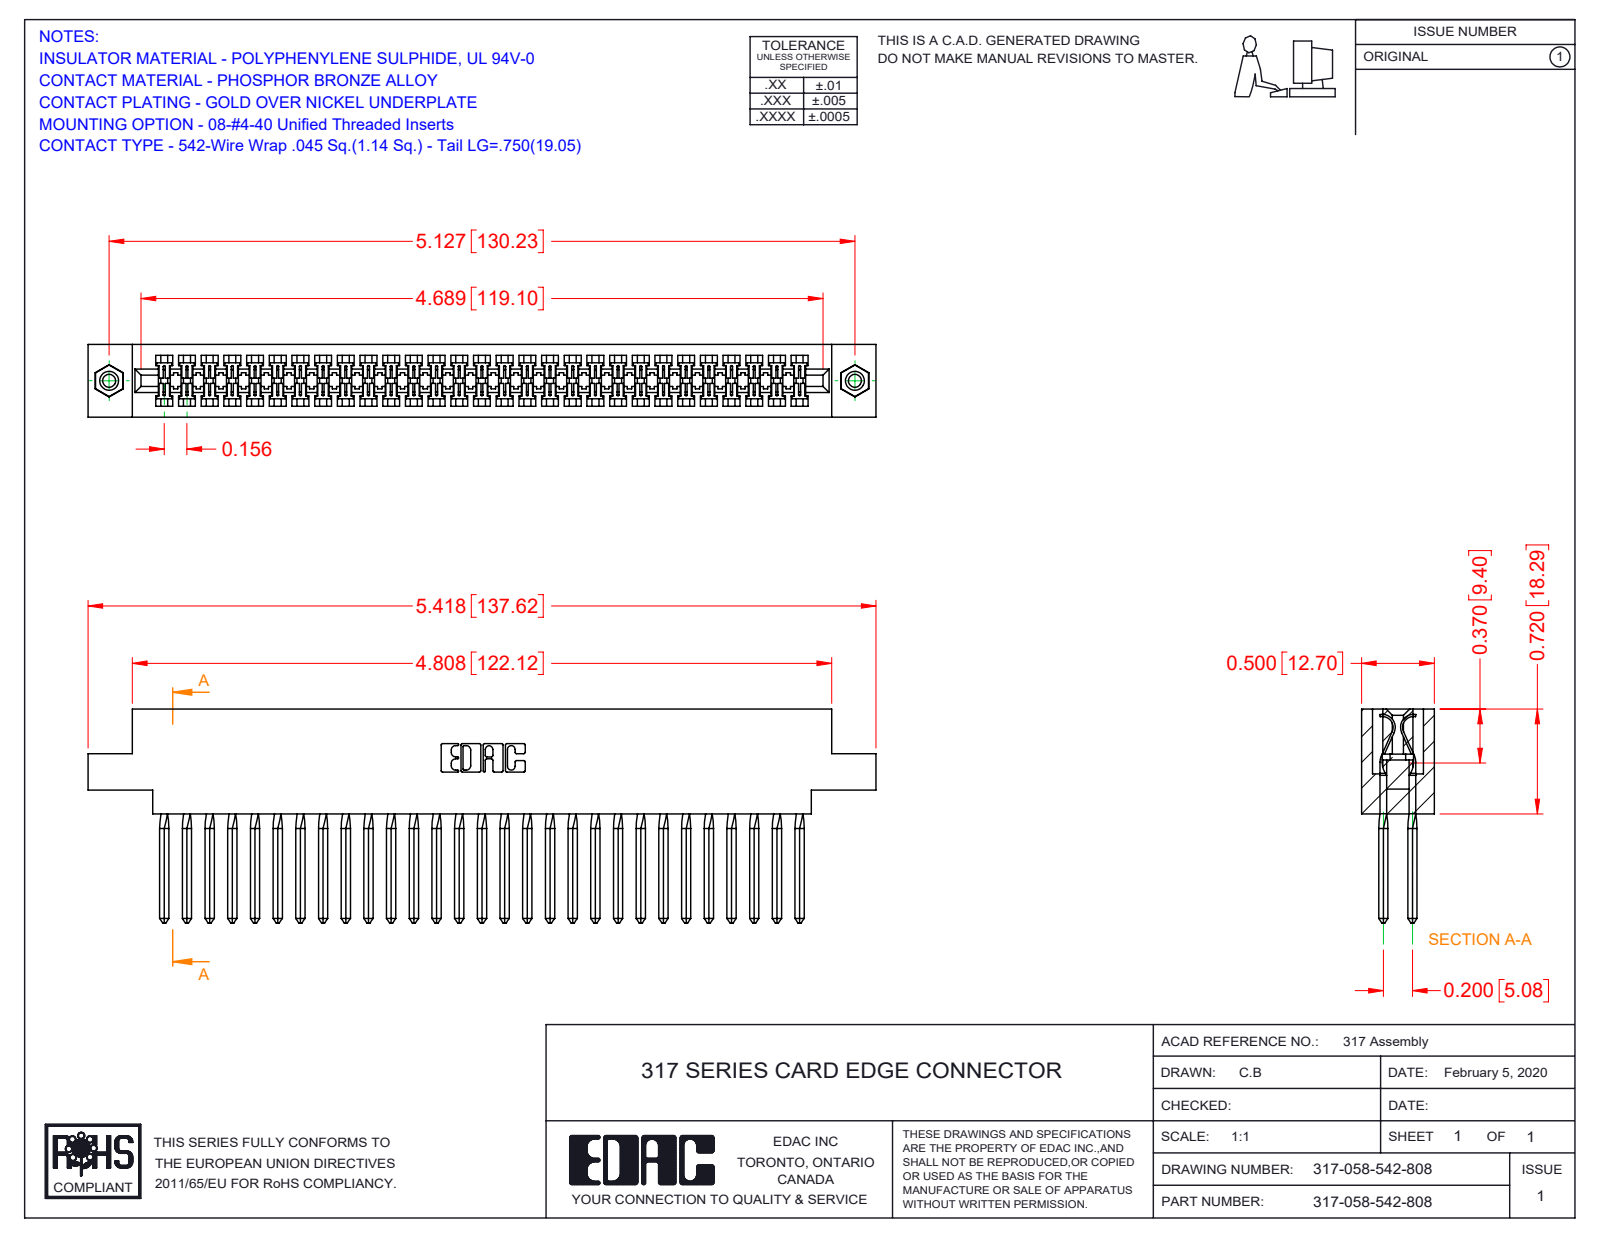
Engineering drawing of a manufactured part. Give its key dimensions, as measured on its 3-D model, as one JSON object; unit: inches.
{"part_name": "345-250-001_345-250-003-102; 317-290-003_542; 317-058-542-878; 317 Part_.156 Dia - TI", "step_written_by": "SolidWorks 2016 (CONFIG_CONTROL_DESIGN)", "units": "inches", "bodies": {"solids": 61, "faces": 3468, "planar": 2758, "cylindrical": 462, "other": 248}, "overall_size": [5.418, 1.47, 0.5], "volume_in3": 1.35, "surface_area_in2": 47.06, "round_holes": [[0.089, 2], [0.125, 2], [0.156, 2]], "round_bosses_or_shafts": [[0.155, 2]], "partial_cylinders_radius": [[0.006, 116], [0.01, 22], [0.007, 6], [0.031, 6], [0.026, 3], [0.074, 2], [0.089, 2], [0.1, 2]], "face_to_face_distances": [0.5, 0.075, 0.425, 0.35, 0.2, 0.11, 0.046, 0.116, 0.136, 0.128], "hole_center_spacings": [5.127]}
